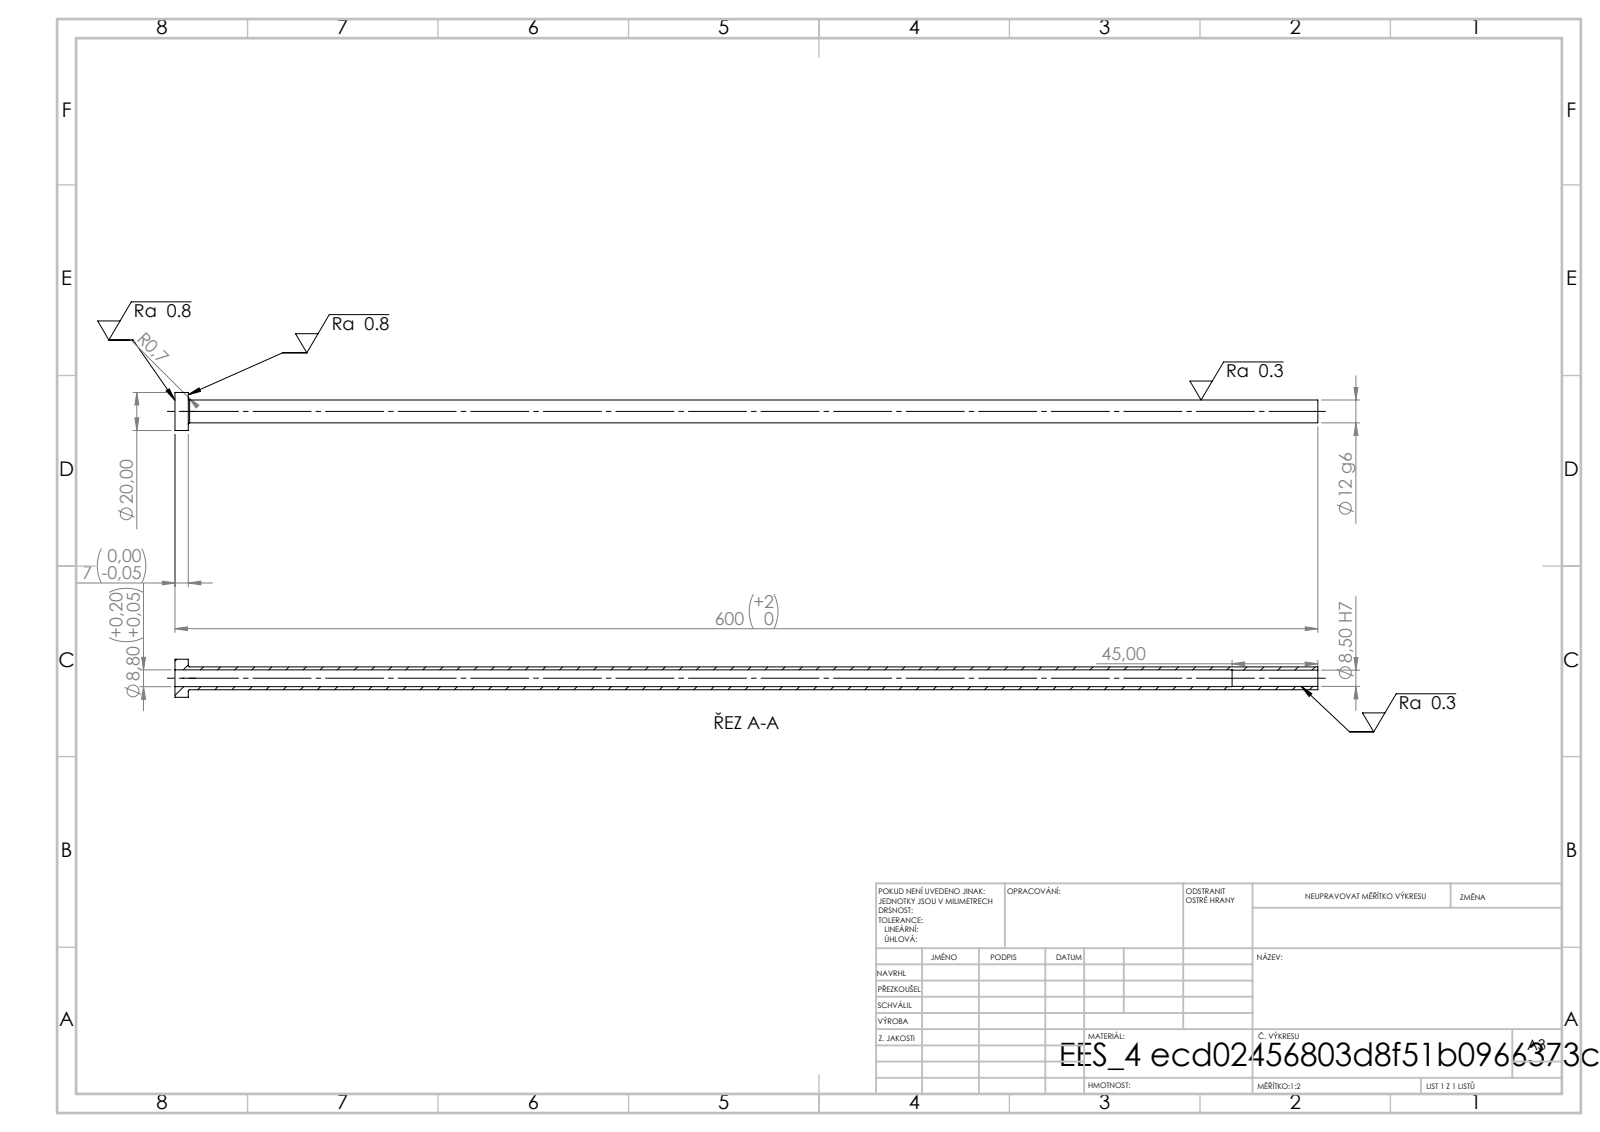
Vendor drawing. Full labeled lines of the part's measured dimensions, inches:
STEP written by: SolidWorks 2019 (CONFIG_CONTROL_DESIGN)
Units: inches
Bodies: 1 solid, 14 faces (4 planar, 8 cylindrical, 2 other)
Overall size (bounding box): 23.622 × 0.787 × 0.787
Volume: 2.011 in³ · Surface area: 61.76 in²
Round holes (diameter × count): ⌀0.335 ×1, ⌀0.346 ×1
Round bosses / shafts (diameter × count): ⌀0.787 ×1, ⌀0.472 ×1
Main face-to-face distances: 0.276, 23.622, 23.346, 21.85, 21.575, 1.772
